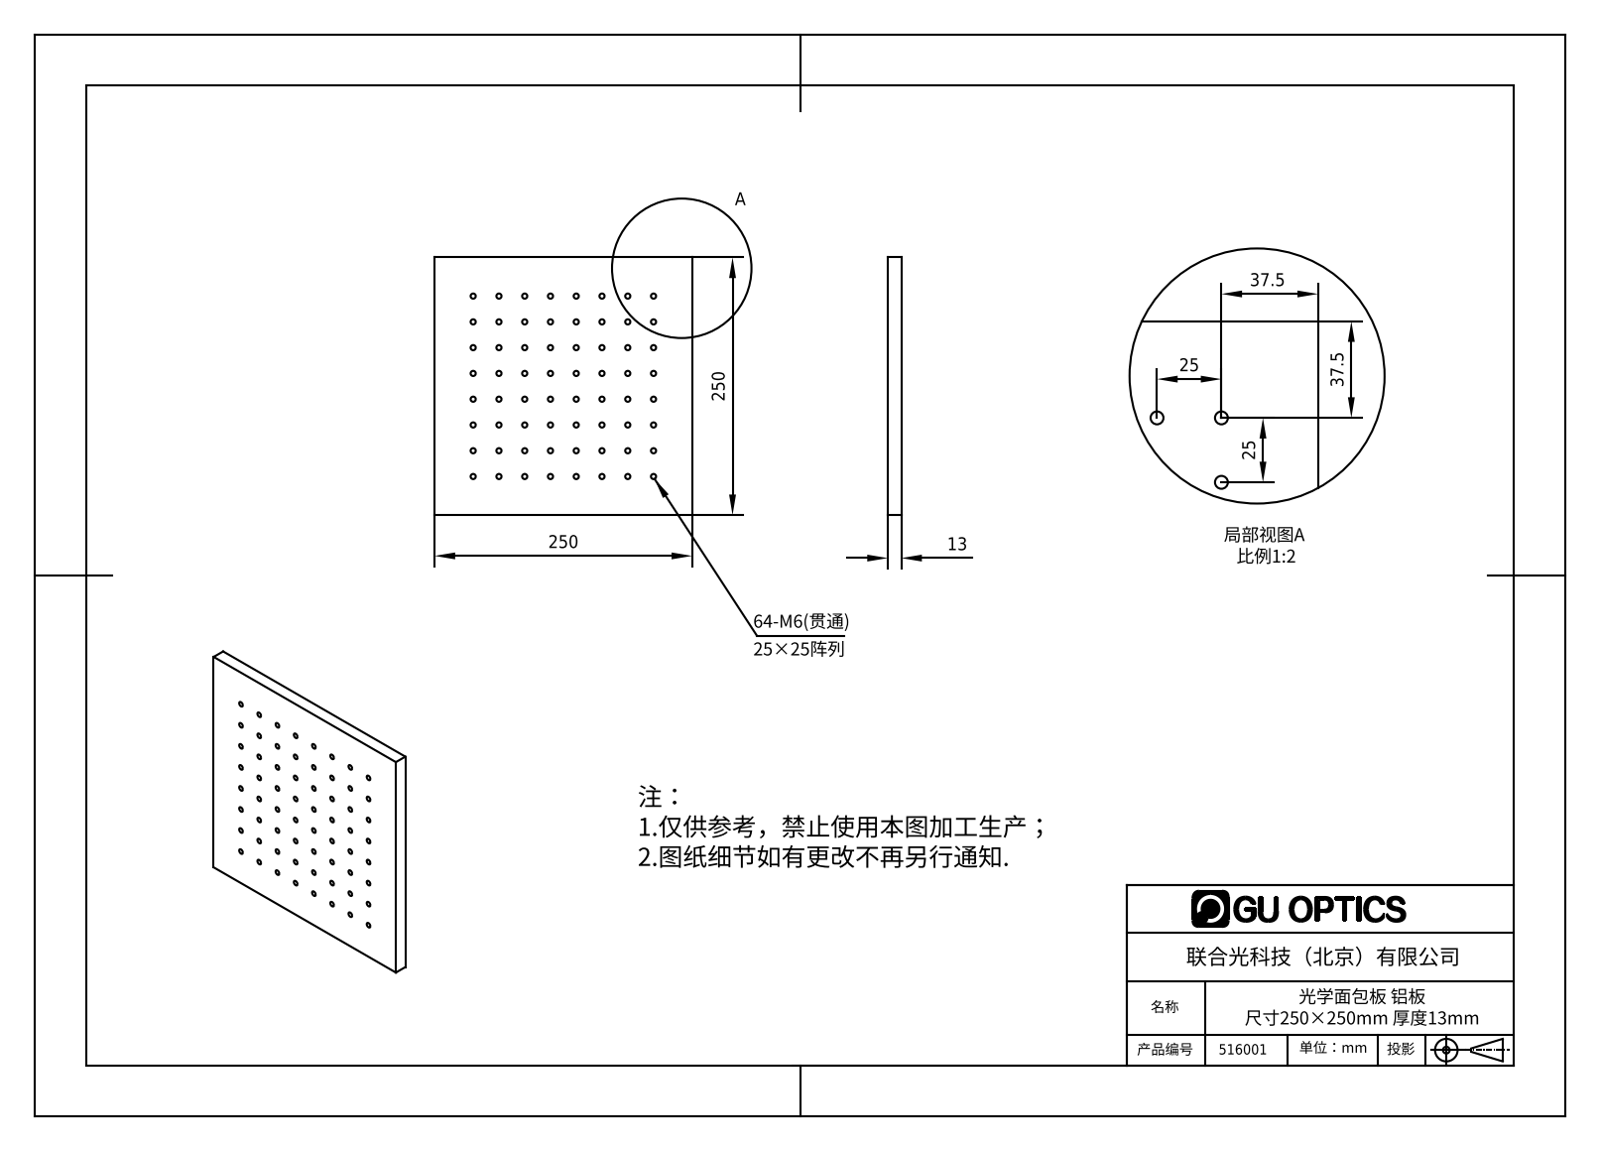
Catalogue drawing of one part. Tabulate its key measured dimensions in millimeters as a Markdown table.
| quantity | value |
| --- | --- |
| part name | 516001 |
| STEP written by | SolidWorks 2016 (AUTOMOTIVE_DESIGN) |
| units | millimeters |
| bodies | 1 solid, 134 faces (6 planar, 128 cylindrical, 0 other) |
| overall size | 250 × 250 × 13 |
| volume | 796 164 mm³ |
| surface area | 148 556 mm² |
| round holes (diameter × count) | 5 × 64 |
| main face-to-face distances | 13, 250 |
| hole center spacings | 55.9, 25, 79.06, 35.36, 50, 90.14, 103.08, 70.71 |
